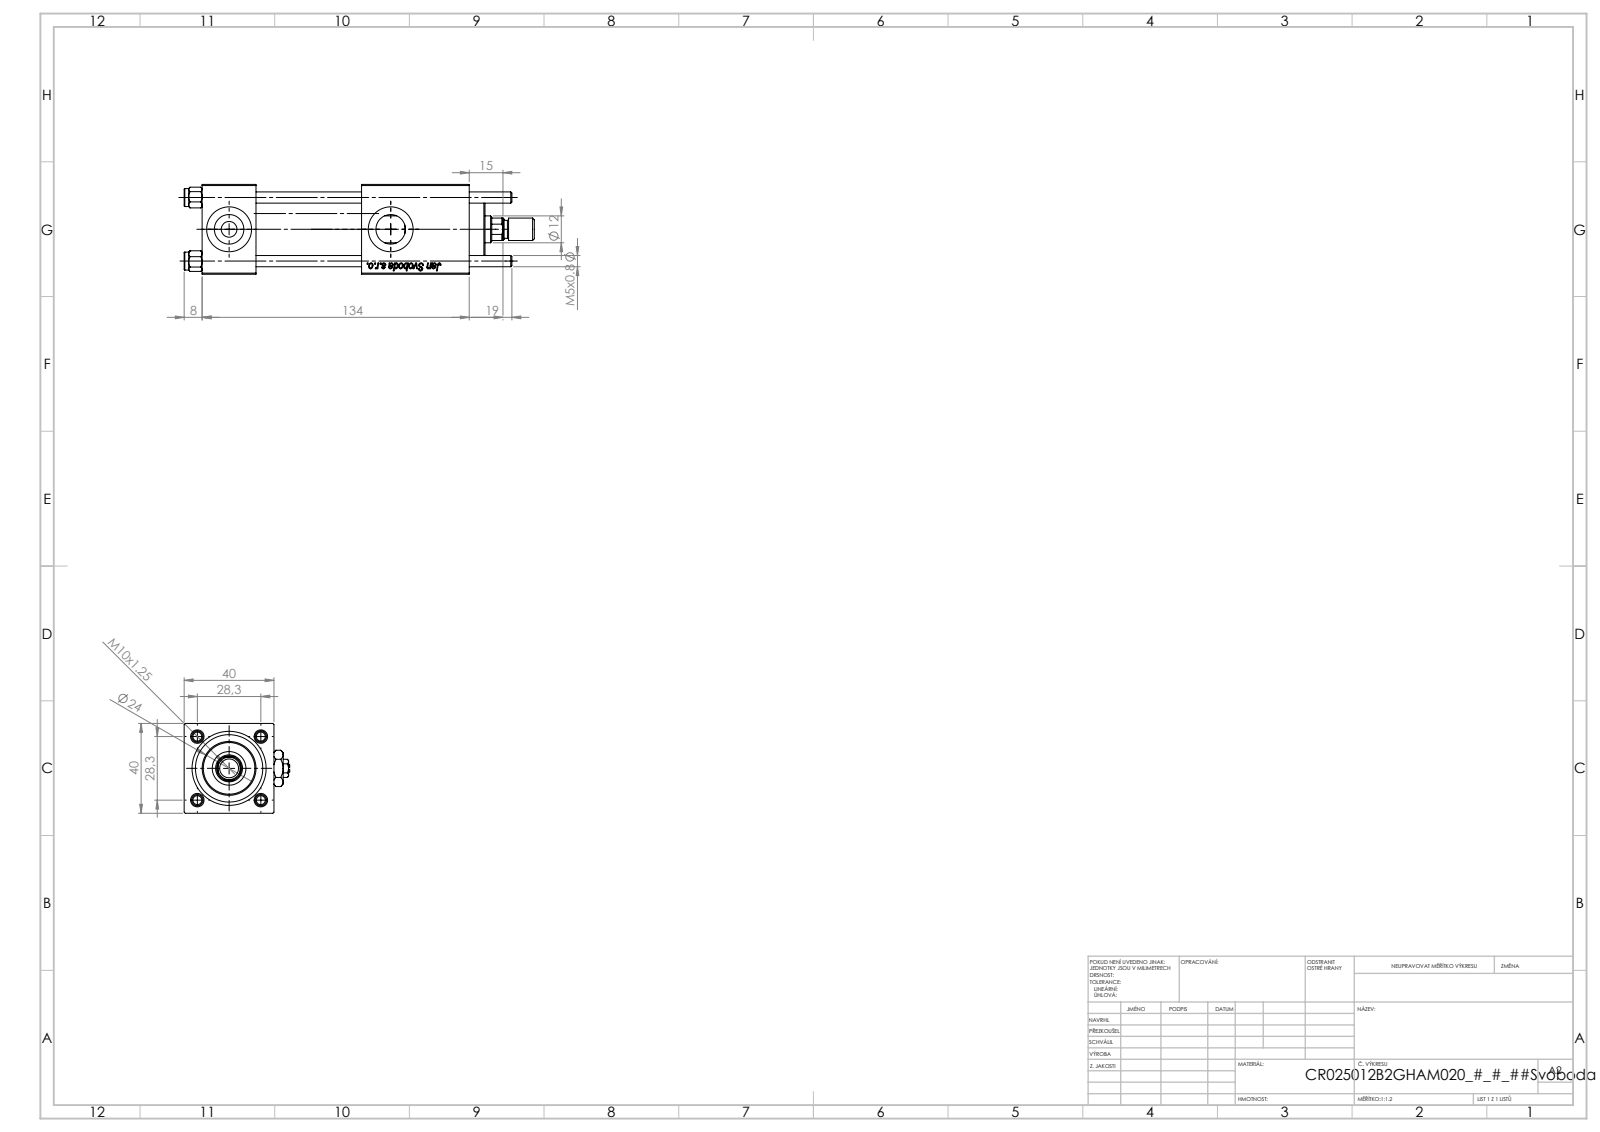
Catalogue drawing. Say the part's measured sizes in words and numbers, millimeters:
The part is named "V215CR_VCP_B; V215CR_B-1; NUT_M5_B; V215_VC_A (+3 more)". Its 3-D file was written by "SolidWorks 2019 (CONFIG_CONTROL_DESIGN)". It is 13 solids with 1222 faces: 456 planar, 90 cylindrical and 676 other. Overall it measures 156 by 47 by 40 millimeters. Its volume is 145 162 cubic millimeters and its surface area 60 254 square millimeters. Round holes: 4 of diameter 5, 3 of diameter 20, 2 of diameter 7, 2 of diameter 13.16, 1 of diameter 6.5, 1 of diameter 12, 1 of diameter 15, 1 of diameter 25, 1 of diameter 30. Round bosses or shafts: 5 of diameter 8, 1 of diameter 31, 1 of diameter 24, 1 of diameter 10. Partial cylindrical surfaces (rounded edges, fillets, slot ends): 1 of radius 5.5. The main face-to-face distances are 40, 24, 90.3, 66.3, 119, 47, 71, 19.3, 95, 48. The hole center spacings are 20.01, 28.3, 40.02, 72.
